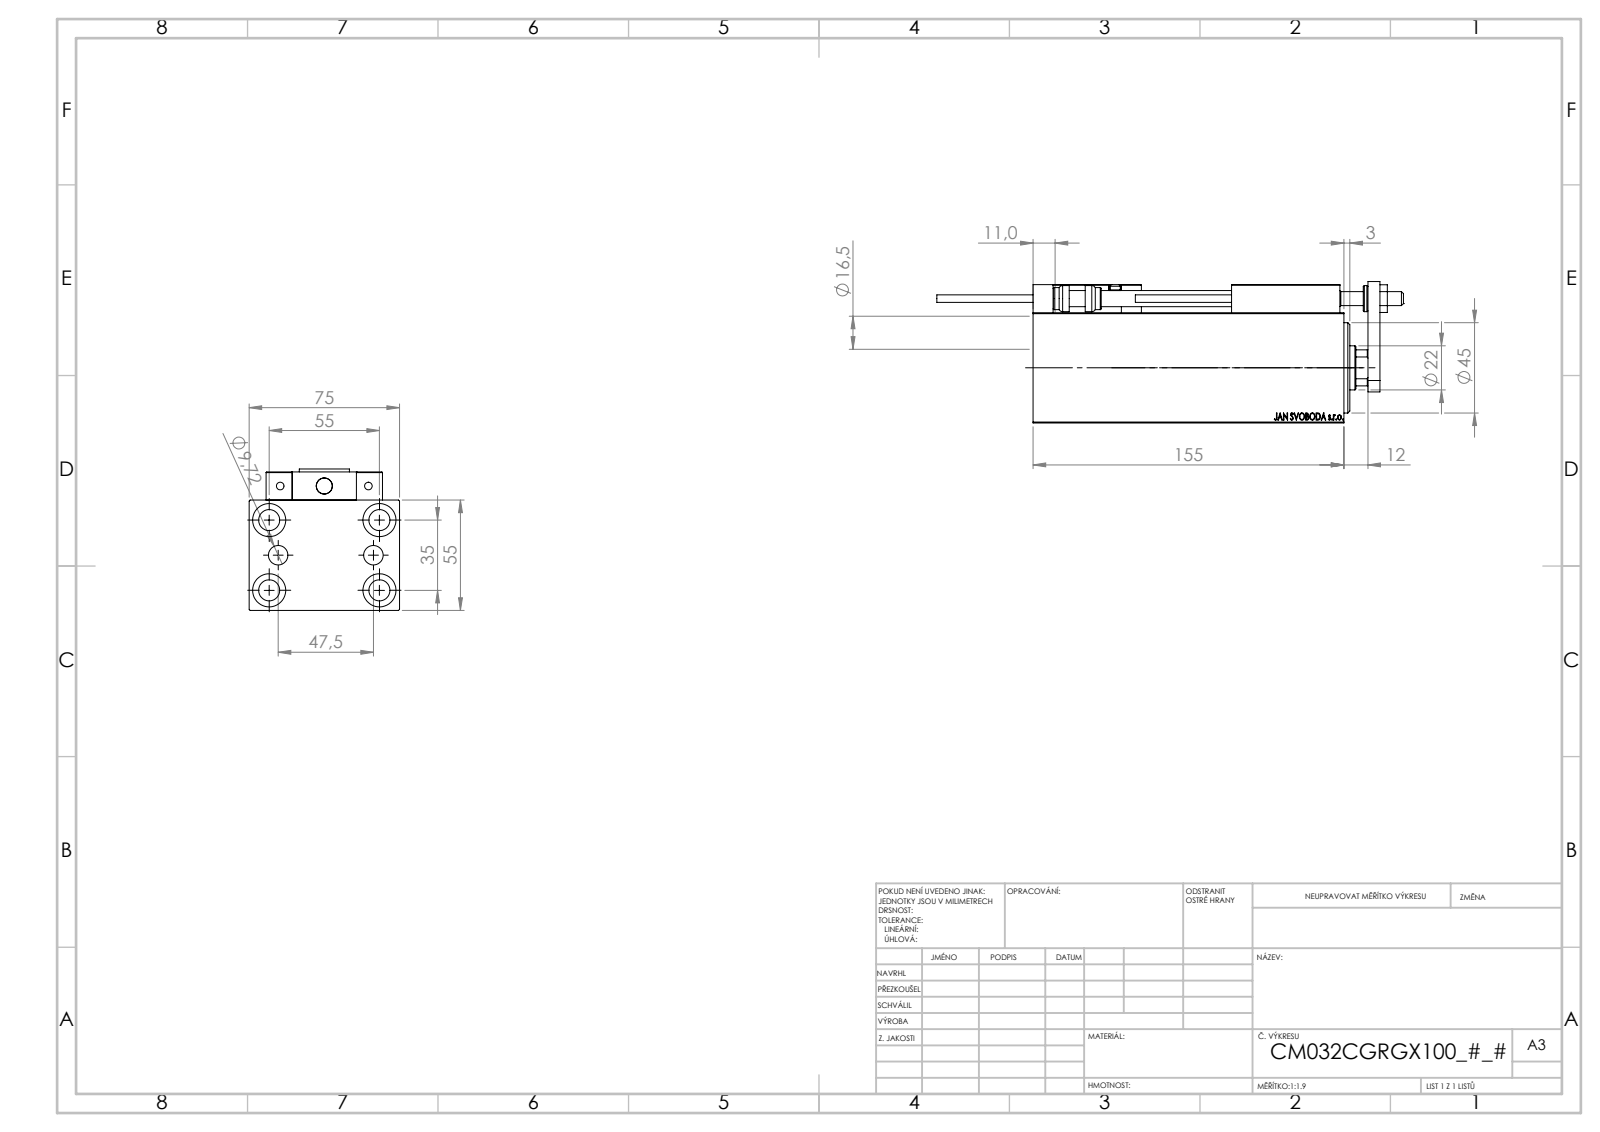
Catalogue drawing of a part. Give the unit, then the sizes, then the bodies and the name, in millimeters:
Units: millimetres
Overall size (bounding box): 232.7 × 75 × 70.5
Round holes (diameter × count): ⌀4 ×6, ⌀8 ×5, ⌀10.5 ×5, ⌀16.5 ×5, ⌀3.2 ×4, ⌀5 ×2, ⌀9.72 ×2, ⌀7 ×1, ⌀22 ×1, ⌀25.5 ×1, ⌀32 ×1, ⌀34 ×1
Round bosses / shafts (diameter × count): ⌀5 ×2, ⌀3.8 ×2, ⌀13 ×1, ⌀11 ×1
Partial cylindrical surfaces — rounded edges, fillets, slot ends (radius × count): R0.3 ×30, R3 ×2, R10.5 ×1
Main face-to-face distances: 55, 75, 14, 5, 69, 10, 12, 25, 45, 3
Hole centre spacings: 17.9, 32.6, 54.16, 11.37, 20, 23.75, 29.59, 29.69
Volume: 584 336 mm³ · Surface area: 130 150 mm²
Bodies: 23 solids, 1278 faces (560 planar, 184 cylindrical, 534 other)
Part name (STEP PRODUCT): SWITCH DIM B,W; NUT_D12; ZARAZKA; V450CM_C_VCP (+7 more)
STEP written by: SolidWorks 2019 (CONFIG_CONTROL_DESIGN)
